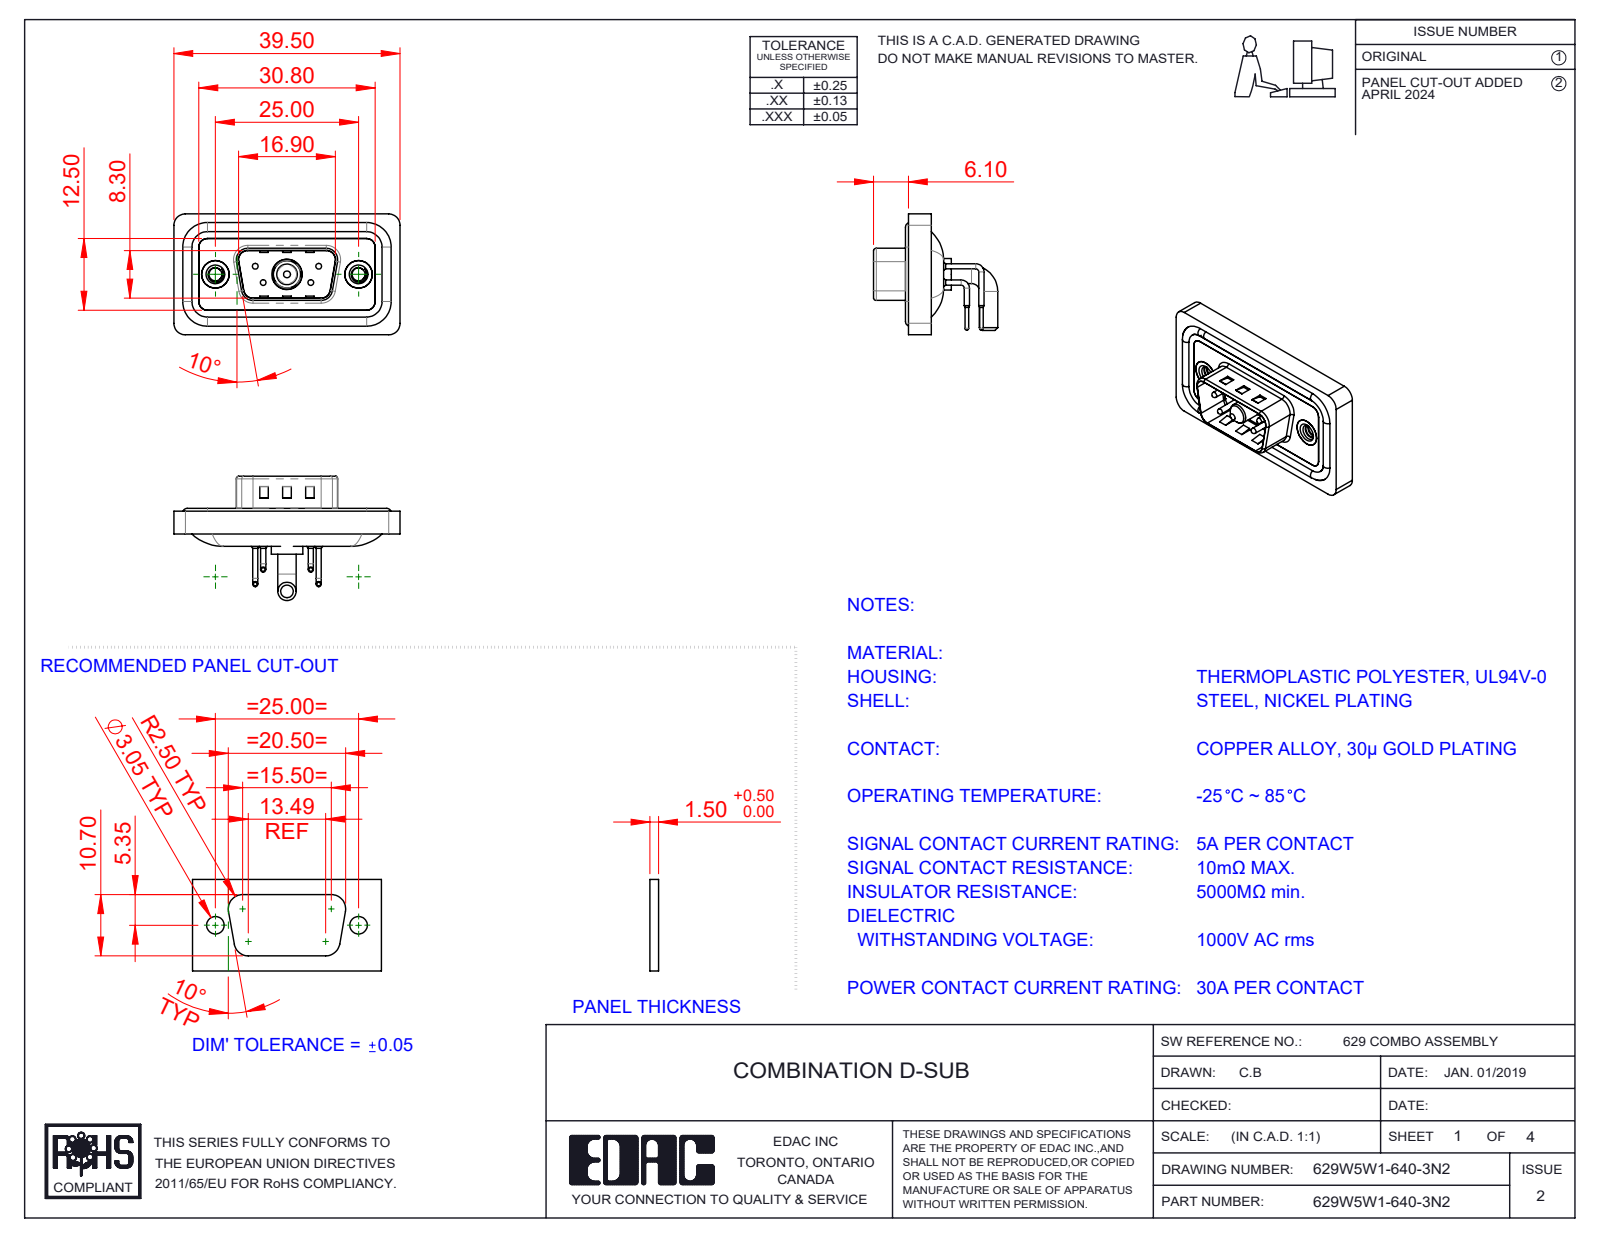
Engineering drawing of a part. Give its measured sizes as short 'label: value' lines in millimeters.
name: 629Combo Contact Row 1; 629Combo Housing_5W1; 629Combo Shell Rear_09 Contacts; 629Combo Threaded Rivet_2 (+5 more)
written by: SolidWorks 2023 (CONFIG_CONTROL_DESIGN)
unit: mm
bodies: 13 solids, 894 faces (411 planar, 345 cylindrical, 138 other)
size: 39.5 × 21.7 × 21.1
volume: 4 515 mm³; area: 7 183 mm²
holes: 4× ⌀0.75, 4× ⌀1.6, 4× ⌀2, 2× ⌀2.26, 2× ⌀4, 2× ⌀4.8, 2× ⌀5, 1× ⌀4.85, 1× ⌀5.3
bosses: 8× ⌀0.9, 4× ⌀1.6, 4× ⌀1.5, 4× ⌀1, 4× ⌀0.65, 2× ⌀4.9, 2× ⌀3.2, 1× ⌀5.5
rounds: 18× R1.5, 18× R2, 8× R0.5, 8× R1.6, 4× R0.25, 4× R0.6, 4× R0.65, 4× R0.9
face distances: 0.4, 2.9, 1.1, 0.8, 2.1, 2.5, 1.6, 3.1, 4.5, 1.5
hole spacings: 3.16, 5.72, 7.1, 12.5, 18.1, 4.39, 4.4, 8.31
